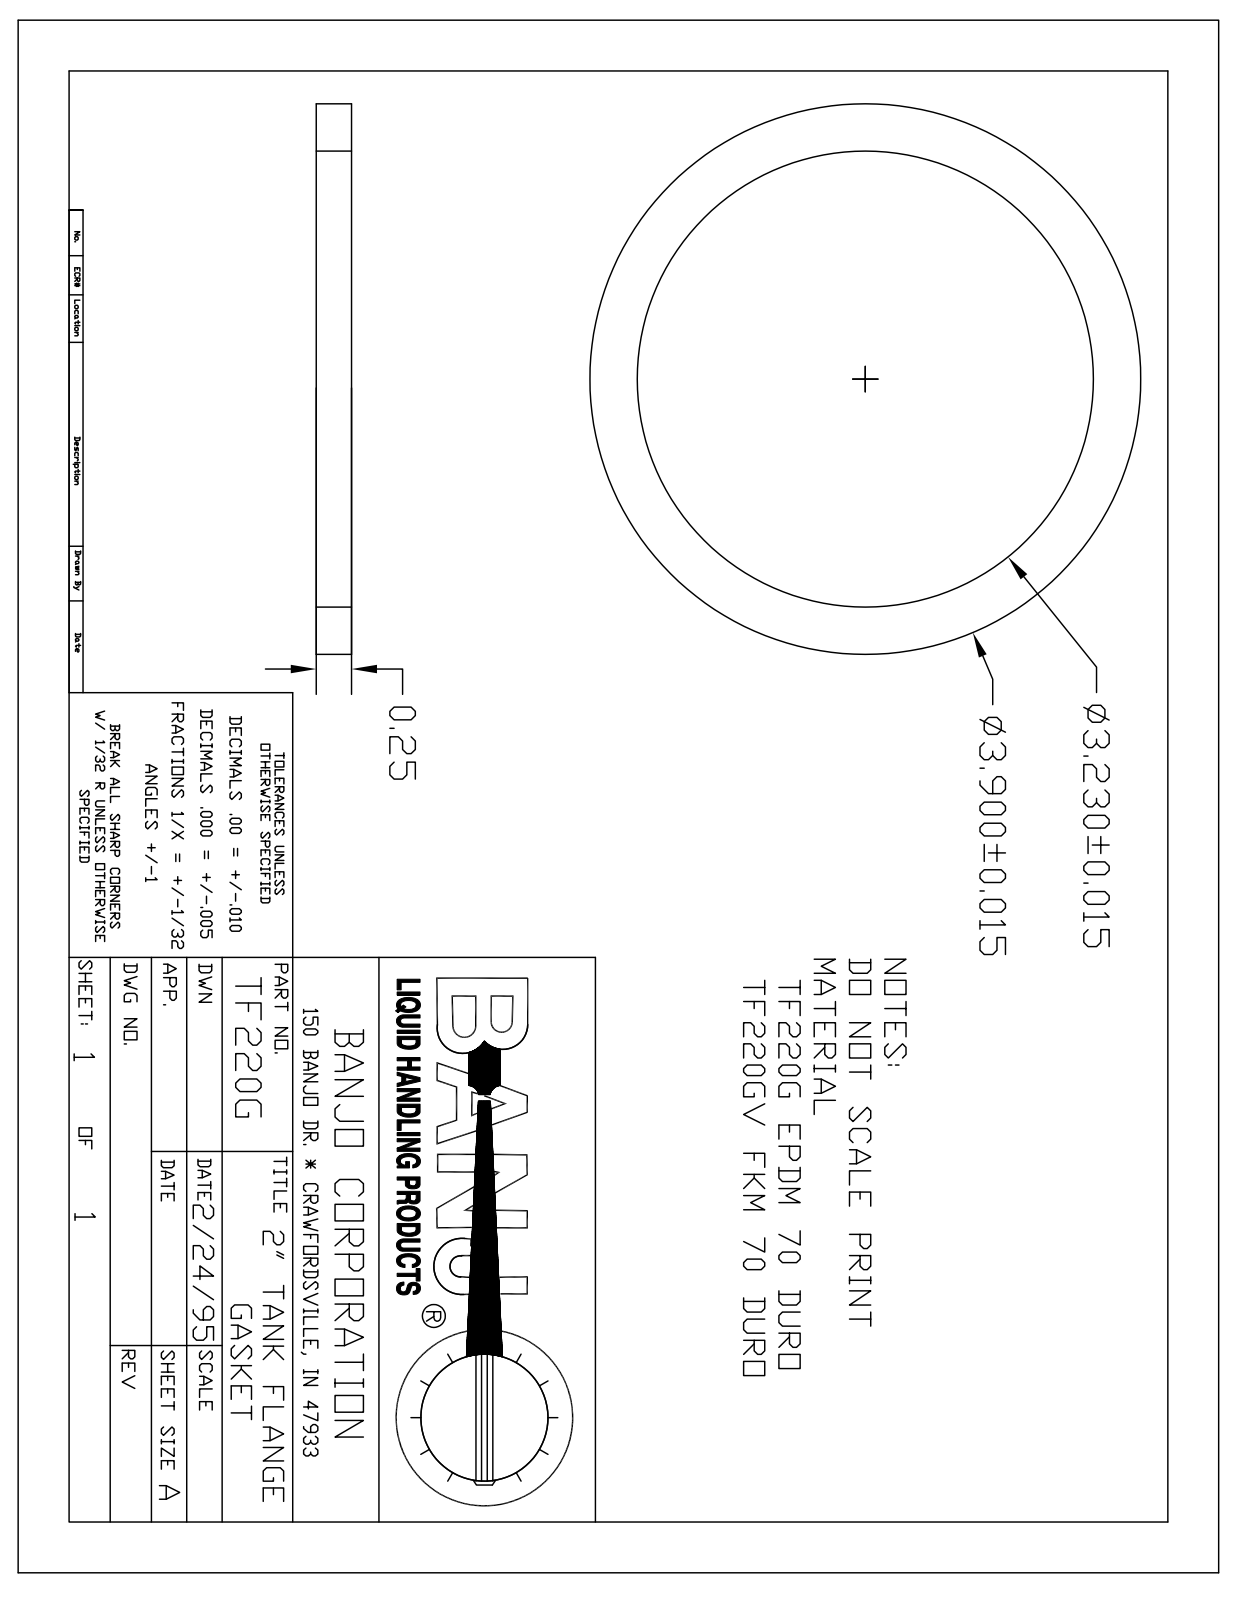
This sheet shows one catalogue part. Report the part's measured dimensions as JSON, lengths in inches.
{"part_name": "TF220G", "step_written_by": "Autodesk Inventor 2013 (AUTOMOTIVE_DESIGN)", "units": "inches", "bodies": {"solids": 1, "faces": 4, "planar": 2, "cylindrical": 2, "other": 0}, "overall_size": [3.9, 3.9, 0.25], "volume_in3": 0.938, "surface_area_in2": 13.1, "round_holes": [[3.23, 1]], "round_bosses_or_shafts": [[3.9, 1]], "face_to_face_distances": [0.25]}
